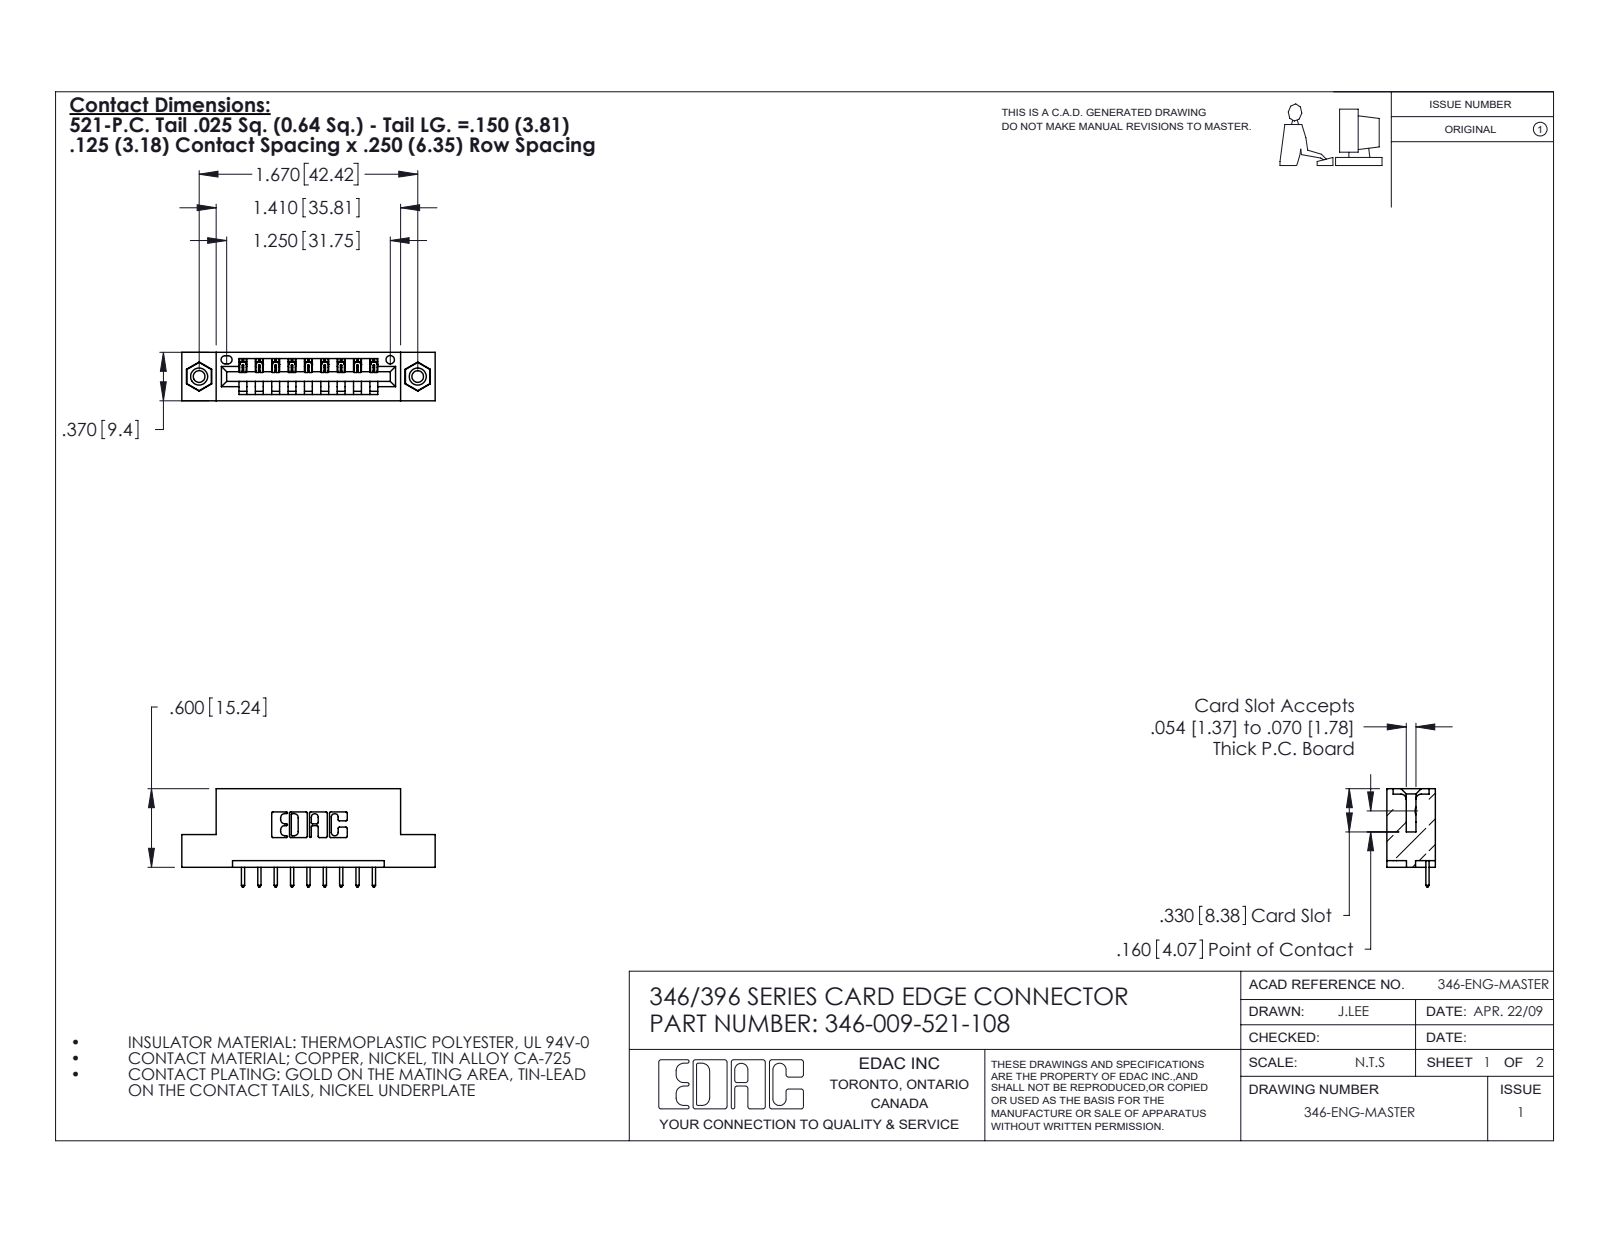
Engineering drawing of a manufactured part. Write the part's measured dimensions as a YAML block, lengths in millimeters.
part_name: "345-292-001_345-293-121; 346 Part_Flush Mounting Lugs - 0.156 Dia-TI; 346-009-521-108; 345-250-001_345-250-003-102"
step_written_by: "SolidWorks 2020 (CONFIG_CONTROL_DESIGN)"
units: millimeters
bodies: {solids: 12, faces: 704, planar: 468, cylindrical: 220, other: 16}
overall_size: [49.1, 19.1, 9.4]
volume: 4440
surface_area: 5120
round_holes:
  - {diameter: 2.3, count: 2}
  - {diameter: 3.2, count: 2}
  - {diameter: 4, count: 2}
  - {diameter: 1.6, count: 1}
round_bosses_or_shafts:
  - {diameter: 3.9, count: 2}
partial_cylinders:
  - {radius: 0.3, count: 22}
  - {radius: 0.2, count: 18}
  - {radius: 0.3, count: 18}
  - {radius: 0.2, count: 6}
  - {radius: 0.8, count: 6}
  - {radius: 0.7, count: 3}
  - {radius: 0.8, count: 2}
  - {radius: 1, count: 2}
face_to_face_distances: [6.4, 9.4, 1.2, 8.2, 3.8, 5.6, 2.5, 4.4, 1.8, 7.6]
hole_center_spacings: [6.2, 37.2, 42.4]
